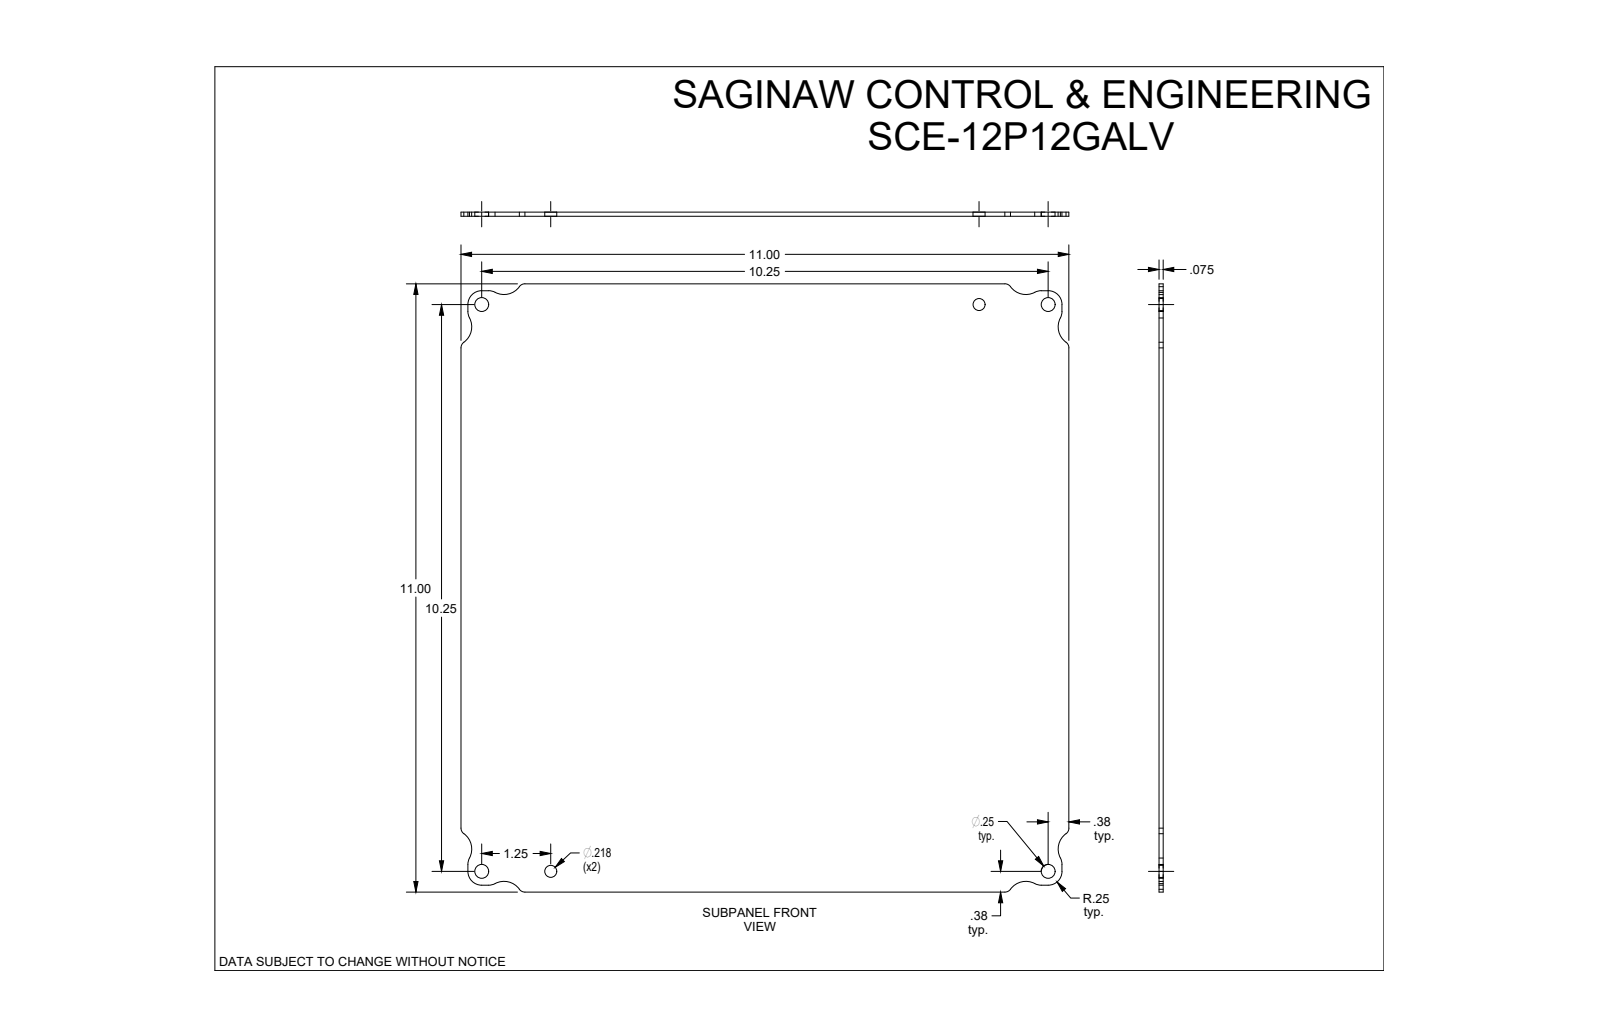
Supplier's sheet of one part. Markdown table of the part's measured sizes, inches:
| quantity | value |
| --- | --- |
| part name | SCE-12P12GALV |
| STEP written by | SolidWorks 2019 (CONFIG_CONTROL_DESIGN) |
| units | inches |
| bodies | 1 solid, 48 faces (14 planar, 34 cylindrical, 0 other) |
| overall size | 11 × 11 × 0.075 |
| volume | 8.965 in³ |
| surface area | 242.6 in² |
| round holes (diameter × count) | 0.25 × 4, 0.218 × 2 |
| partial cylindrical surfaces (radius × count) | 0.25 × 12, 0.125 × 8, 0.344 × 8 |
| main face-to-face distances | 0.075, 11, 0.125, 10.875, 10.75 |
| hole center spacings | 10.25, 1.25, 9, 10.326, 13.64, 14.495, 12.85 |
